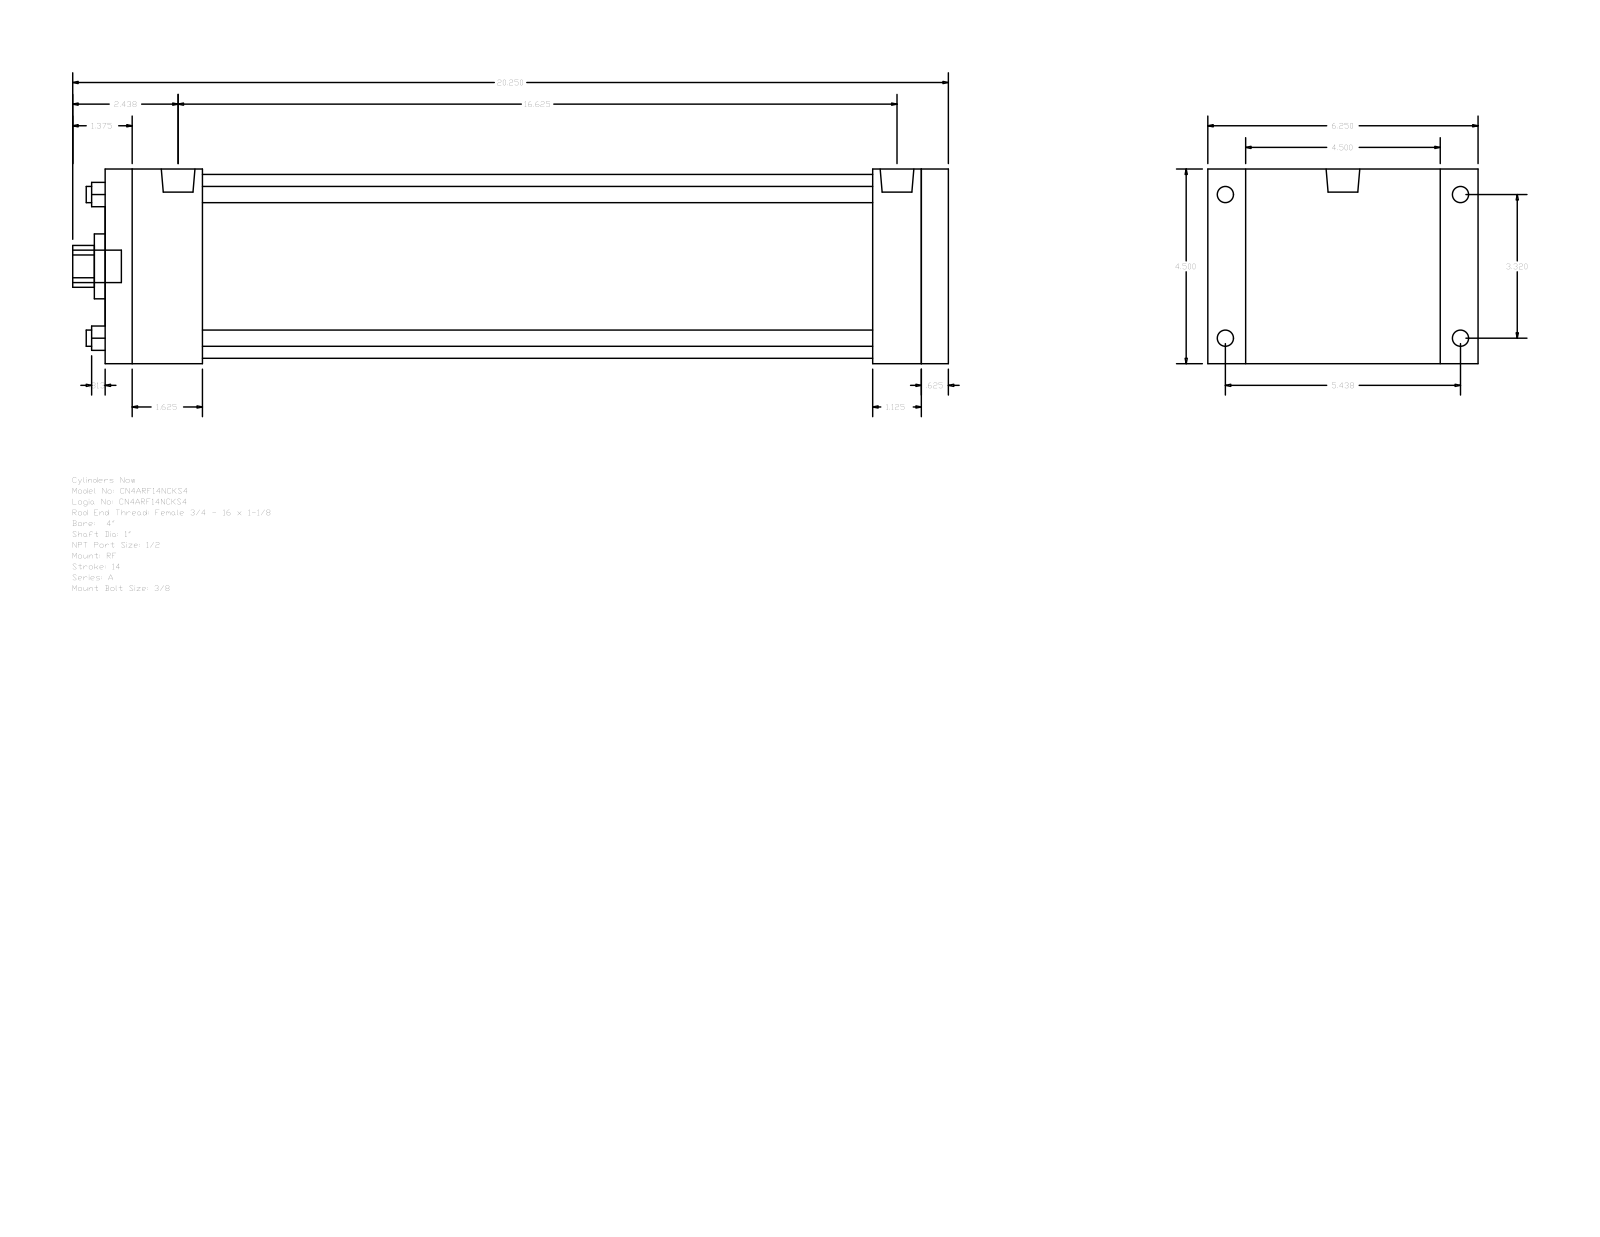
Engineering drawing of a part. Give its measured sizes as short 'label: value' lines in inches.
name: A_RF__0400_1
written by: GSSL Pune (CONFIG_CONTROL_DESIGN)
unit: in
bodies: 0 solids, 92 faces (64 planar, 28 cylindrical, 0 other)
size: 20.25 × 6.25 × 4.5
holes: 4× ⌀0.375, 1× ⌀1, 1× ⌀1.5, 1× ⌀4.25
bosses: 4× ⌀0.375, 4× ⌀0.344, 2× ⌀0.778, 1× ⌀0.75
rounds: 1× R0.484
face distances: 4.5, 19.5, 0.625, 18.875, 0.875, 5.375, 17.75, 1.125, 1.75, 2.25
hole spacings: 2.347, 3.32, 4.695
